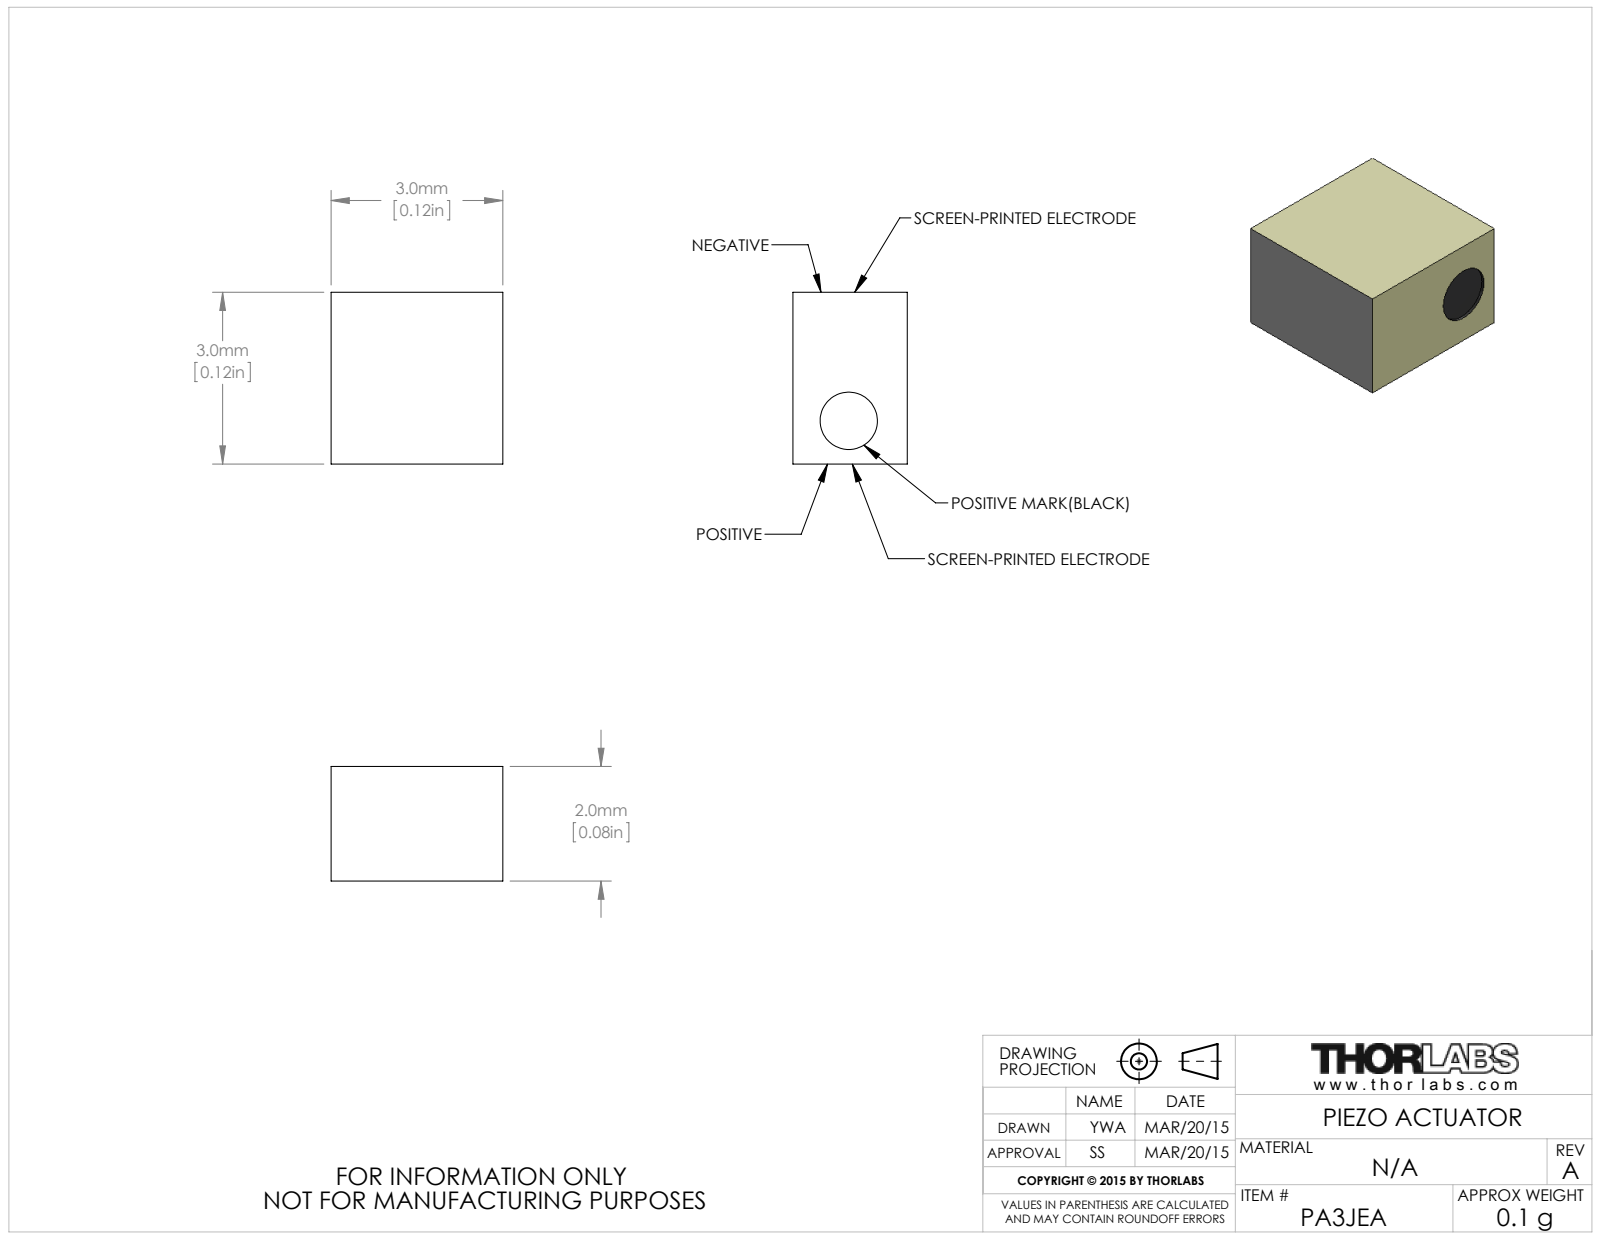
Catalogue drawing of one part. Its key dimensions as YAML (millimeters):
part_name: "CTN002735"
step_written_by: "SolidWorks 2014 (AUTOMOTIVE_DESIGN)"
units: millimeters
bodies: {solids: 1, faces: 9, planar: 7, cylindrical: 2, other: 0}
overall_size: [3, 3, 2]
volume: 18
surface_area: 42
round_holes:
  - {diameter: 1, count: 1}
face_to_face_distances: [3, 2, 2.95]
